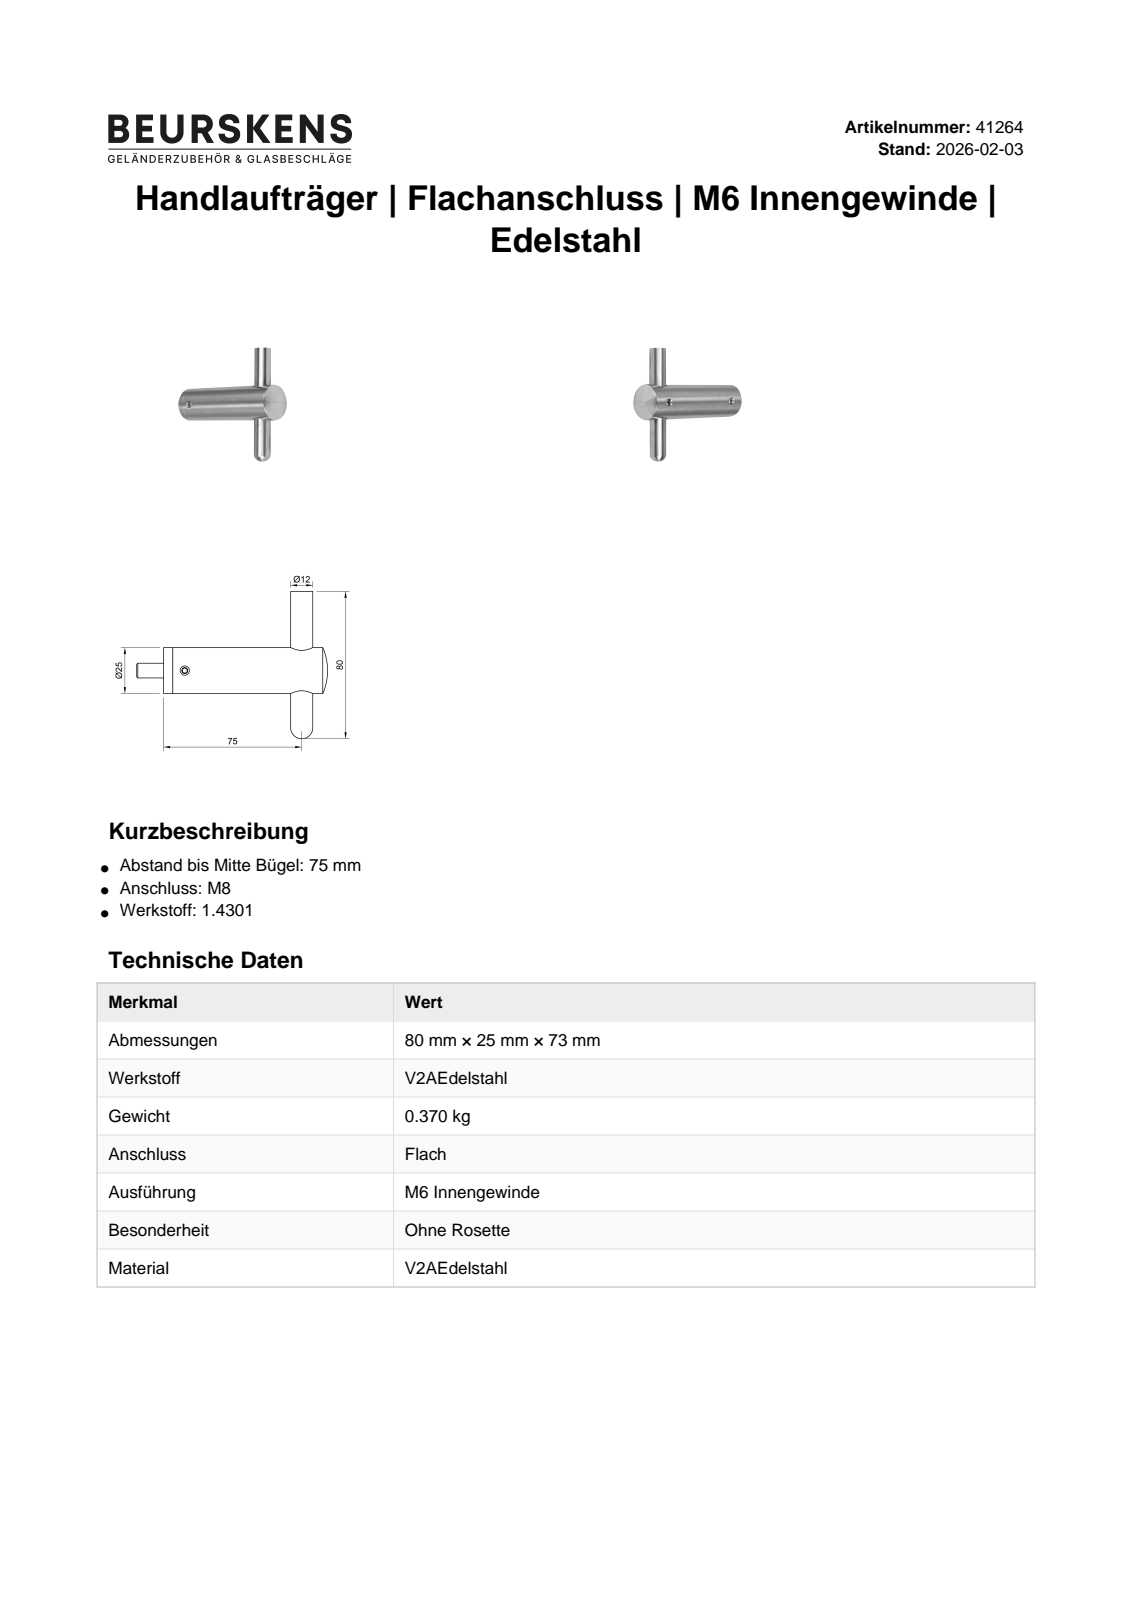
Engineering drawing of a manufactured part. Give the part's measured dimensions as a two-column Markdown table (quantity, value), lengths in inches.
| quantity | value |
| --- | --- |
| part name | 41264; 41264-01; 41264-02; 41264-03 (+2 more) |
| STEP written by | Autodesk Inventor 2022 (AUTOMOTIVE_DESIGN) |
| units | inches |
| bodies | 8 solids, 91 faces (47 planar, 19 cylindrical, 25 other) |
| overall size | 4.079 × 3.15 × 1.029 |
| volume | 2.86 in³ |
| surface area | 26.08 in² |
| round holes (diameter × count) | 0.197 × 2, 0.236 × 1, 0.354 × 1, 0.472 × 1, 0.673 × 1, 0.827 × 1 |
| round bosses / shafts (diameter × count) | 0.984 × 1, 0.669 × 1, 0.63 × 1, 0.315 × 1, 0.197 × 1 |
| main face-to-face distances | 0.098, 0.508, 0.409, 0.197, 0.606, 0.575, 0.673, 0.772, 1.181, 1.283 |
| hole center spacings | 2.5 |
